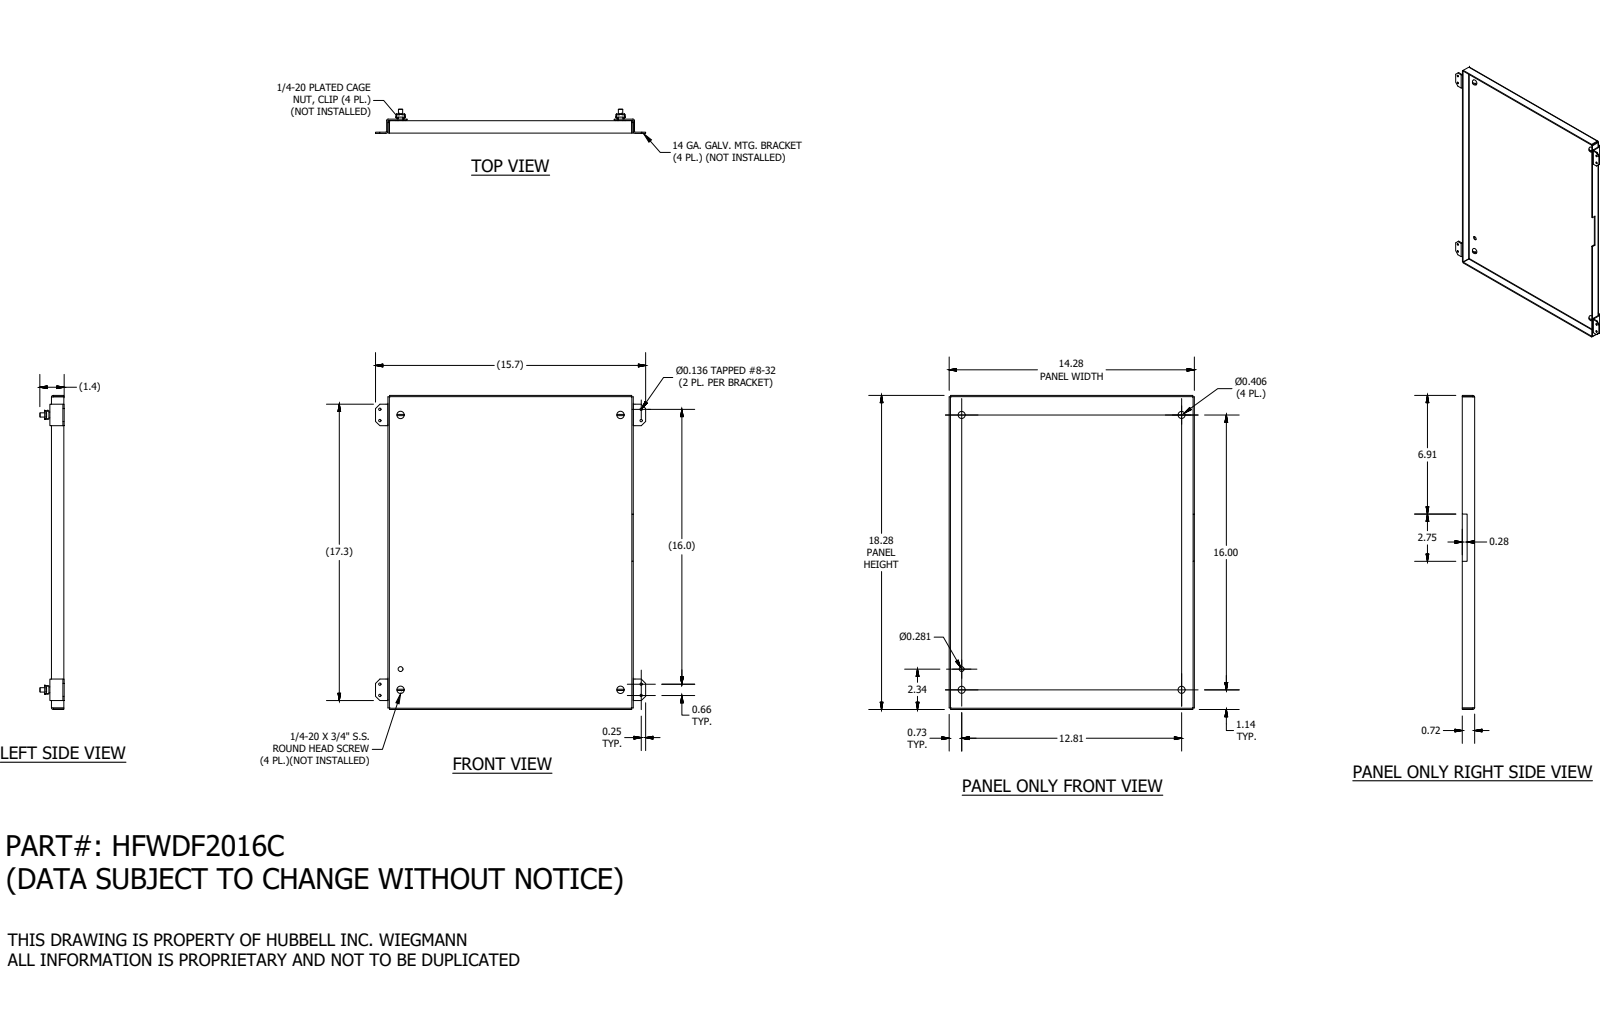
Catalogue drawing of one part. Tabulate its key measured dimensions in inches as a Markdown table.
| quantity | value |
| --- | --- |
| part name | HFWDF2016C |
| STEP written by | SolidWorks 2023 (AUTOMOTIVE_DESIGN) |
| units | inches |
| bodies | 13 solids, 595 faces (418 planar, 161 cylindrical, 16 other) |
| overall size | 18.281 × 15.726 × 1.415 |
| volume | 23.39 in³ |
| surface area | 641.9 in² |
| round holes (diameter × count) | 0.136 × 8, 0.185 × 4, 0.328 × 4, 0.406 × 4, 0.281 × 1 |
| round bosses / shafts (diameter × count) | 0.25 × 4 |
| partial cylindrical surfaces (radius × count) | 0.025 × 20, 0.021 × 16, 0.045 × 12, 0.031 × 8, 0.105 × 8, 0.021 × 4 |
| main face-to-face distances | 0.074, 14.207, 18.207, 14.133, 14.281, 0.094, 18.281, 18.133, 0.078, 14.285 |
| hole center spacings | 1.251, 14.024, 16, 0.66, 15.227, 15.241, 15.717, 16.374 |
